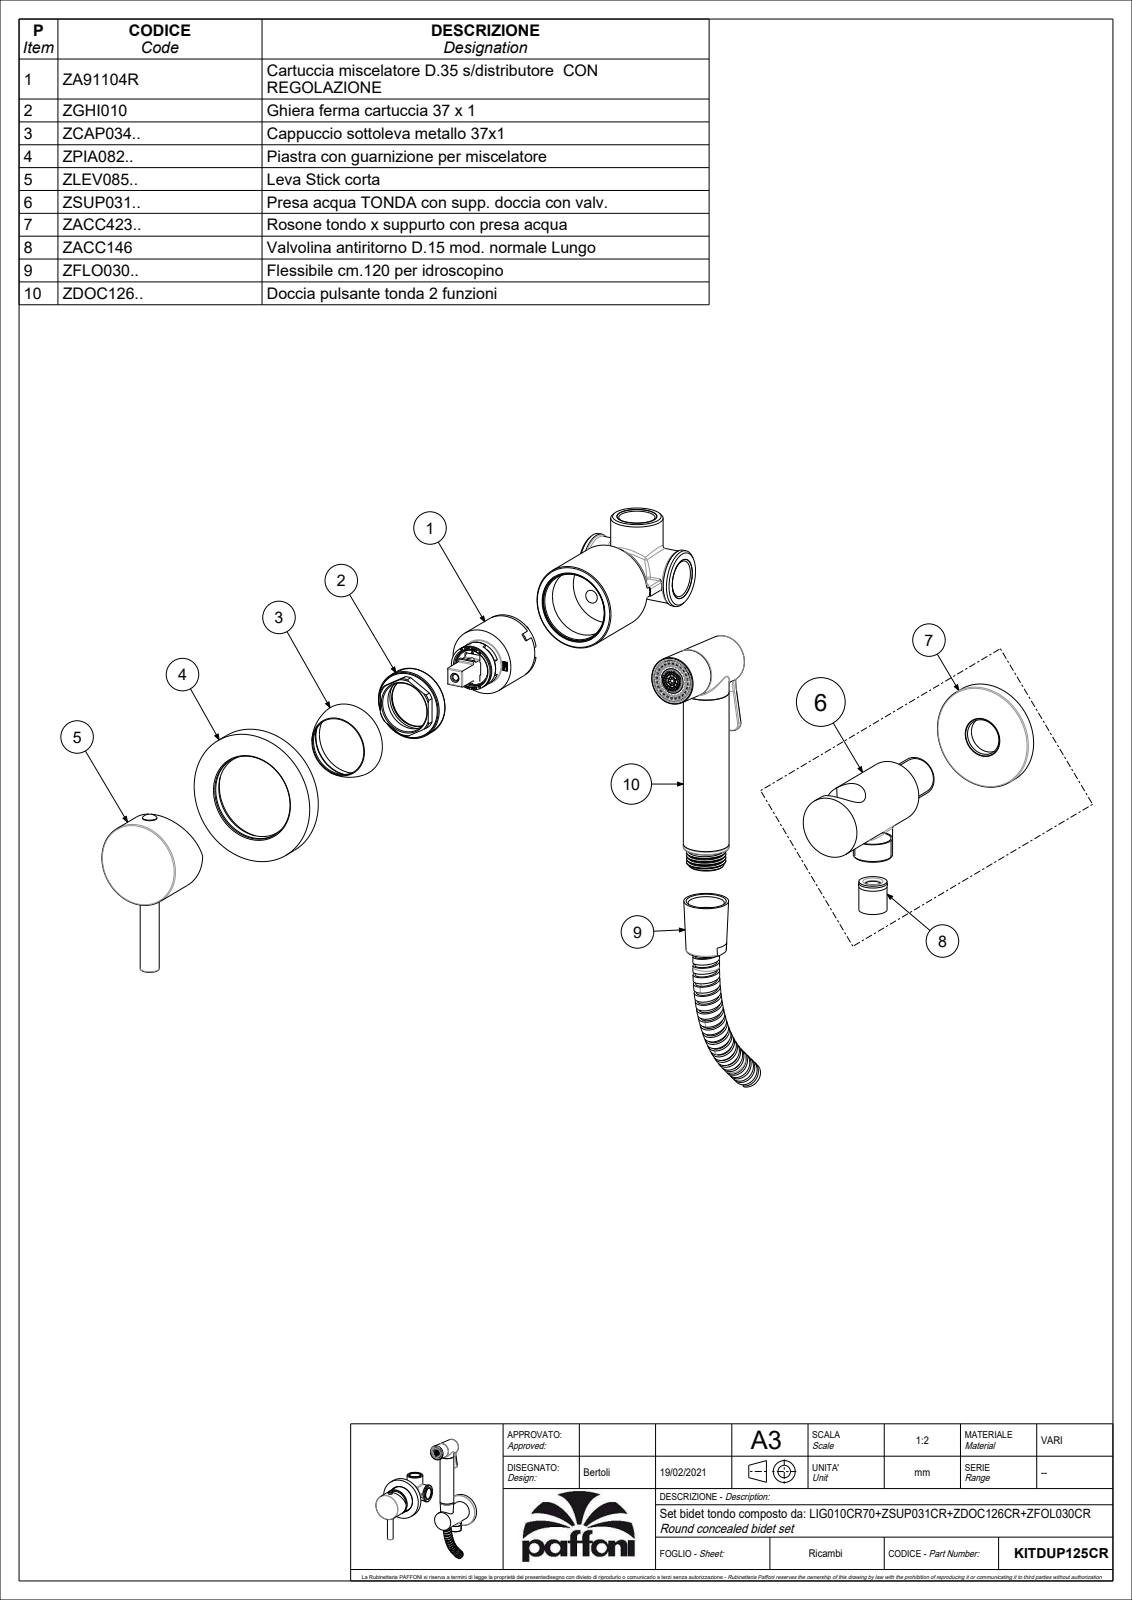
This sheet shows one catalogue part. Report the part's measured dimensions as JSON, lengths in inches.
{"part_name": "KITDUP125CR", "step_written_by": "CREO PARAMETRIC BY PTC INC, 2022124 (CONFIG_CONTROL_DESIGN)", "units": "inches", "bodies": {"solids": 0, "faces": 791, "planar": 233, "cylindrical": 182, "other": 376}, "overall_size": [9.17, 7.185, 3.655], "round_holes": [[0.118, 1], [0.22, 1], [0.335, 1], [0.488, 1], [0.512, 1], [0.748, 1], [1.102, 1], [1.22, 1], [1.417, 1], [1.874, 1], [2.047, 1], [2.559, 1]], "round_bosses_or_shafts": [[2.756, 1], [2.165, 1], [2.15, 1], [1.764, 1], [1.752, 1], [1.28, 1], [1.043, 1], [0.984, 1]], "partial_cylinders_radius": [[0.008, 45], [0.004, 37], [0.02, 14], [0.012, 4], [0.061, 2], [1.181, 2], [0.108, 1], [0.332, 1]], "face_to_face_distances": [0.177, 0.118, 0.059, 0.236, 0.354, 0.079, 0.039, 0.276, 2.559, 0.098], "hole_center_spacings": [4.724, 4.791]}
